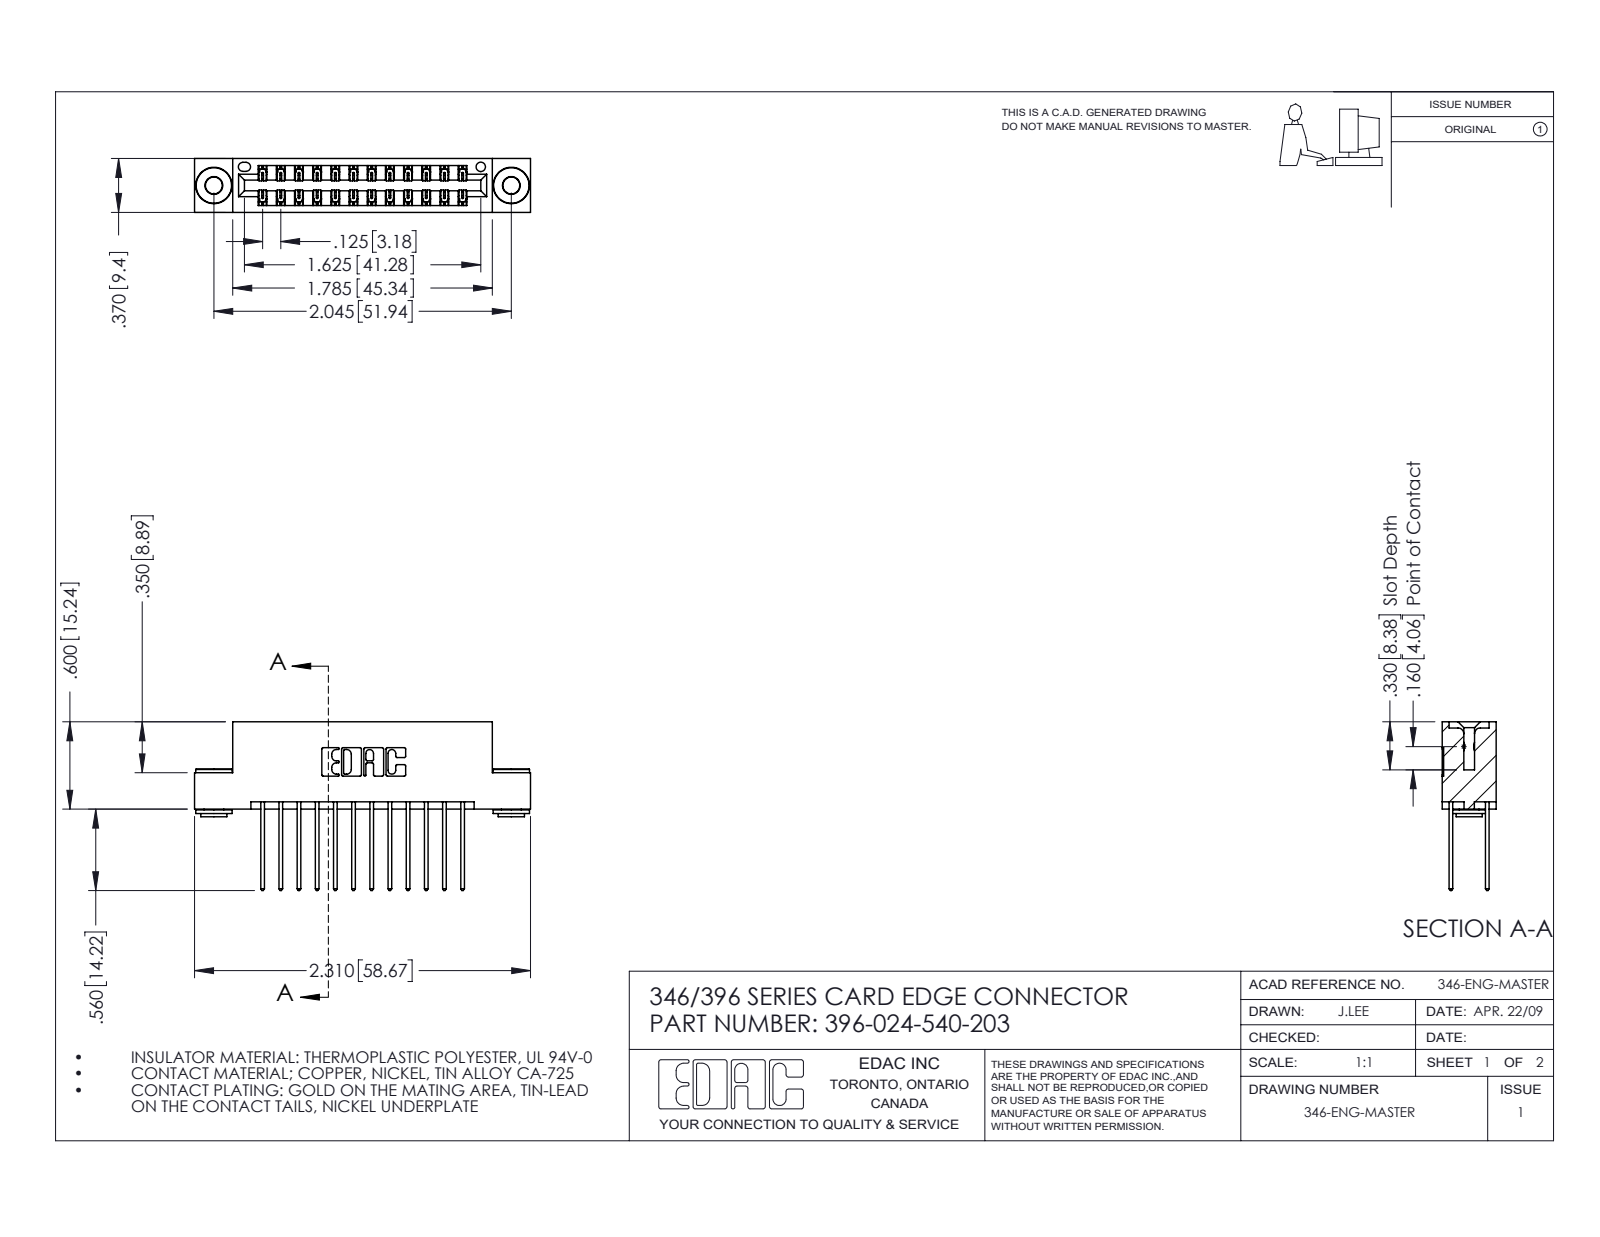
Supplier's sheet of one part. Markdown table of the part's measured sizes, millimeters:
| quantity | value |
| --- | --- |
| part name | 396-024-540-203; 345-250-002_345-250-002-102; 345-292-001_345-293-140; 346 Part_Flush Mounting Lugs - 0.156 Dia-TH |
| STEP written by | SolidWorks 2016 (CONFIG_CONTROL_DESIGN) |
| units | millimeters |
| bodies | 27 solids, 1408 faces (926 planar, 474 cylindrical, 8 other) |
| overall size | 58.7 × 29.5 × 9.4 |
| volume | 5 600 mm³ |
| surface area | 7 871 mm² |
| round holes (diameter × count) | 2.9 × 2, 4 × 2, 1.6 × 1 |
| round bosses / shafts (diameter × count) | 6.4 × 2, 4.6 × 2, 3.5 × 2 |
| partial cylindrical surfaces (radius × count) | 0.2 × 36, 0.3 × 24, 0.3 × 22, 0.2 × 6, 0.8 × 6, 0.7 × 3, 0.4 × 2, 0.6 × 2 |
| main face-to-face distances | 6.4, 1.2, 8.2, 9.4, 0.6, 1.8, 7.6, 7, 3.8, 5.6 |
| hole center spacings | 6.2, 46.7, 51.9 |
